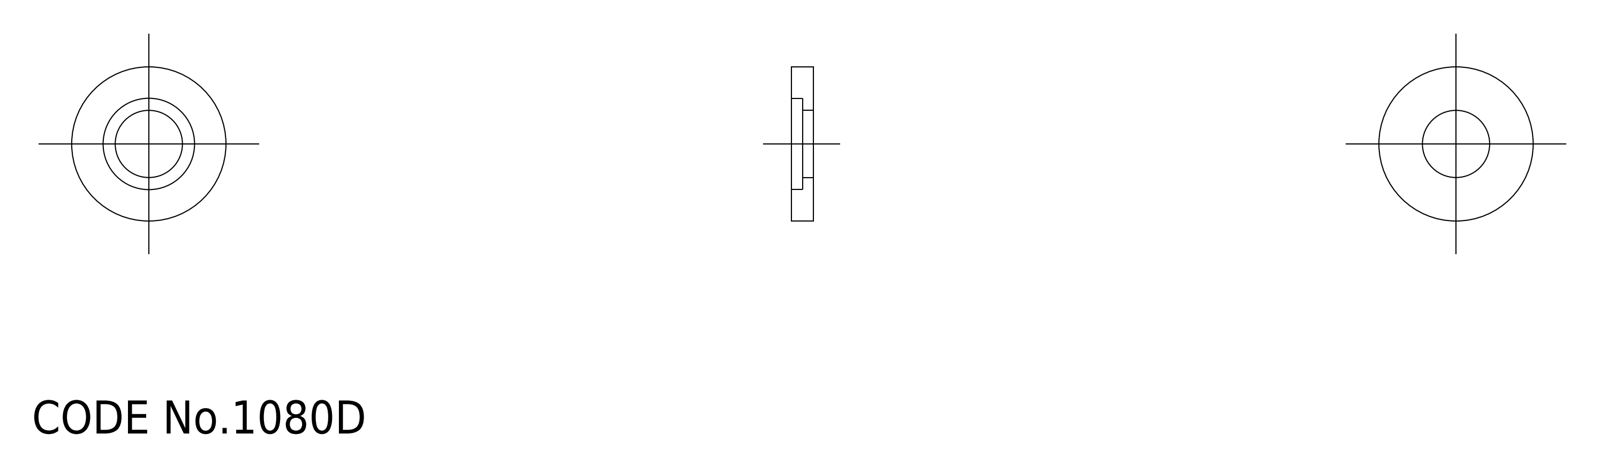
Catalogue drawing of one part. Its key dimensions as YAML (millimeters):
part_name: "washer"
step_written_by: "CADfix (AUTOMOTIVE_DESIGN)"
units: millimeters
bodies: {solids: 1, faces: 9, planar: 0, cylindrical: 0, other: 9}
overall_size: [14, 14, 2]
volume: 225
surface_area: 383
